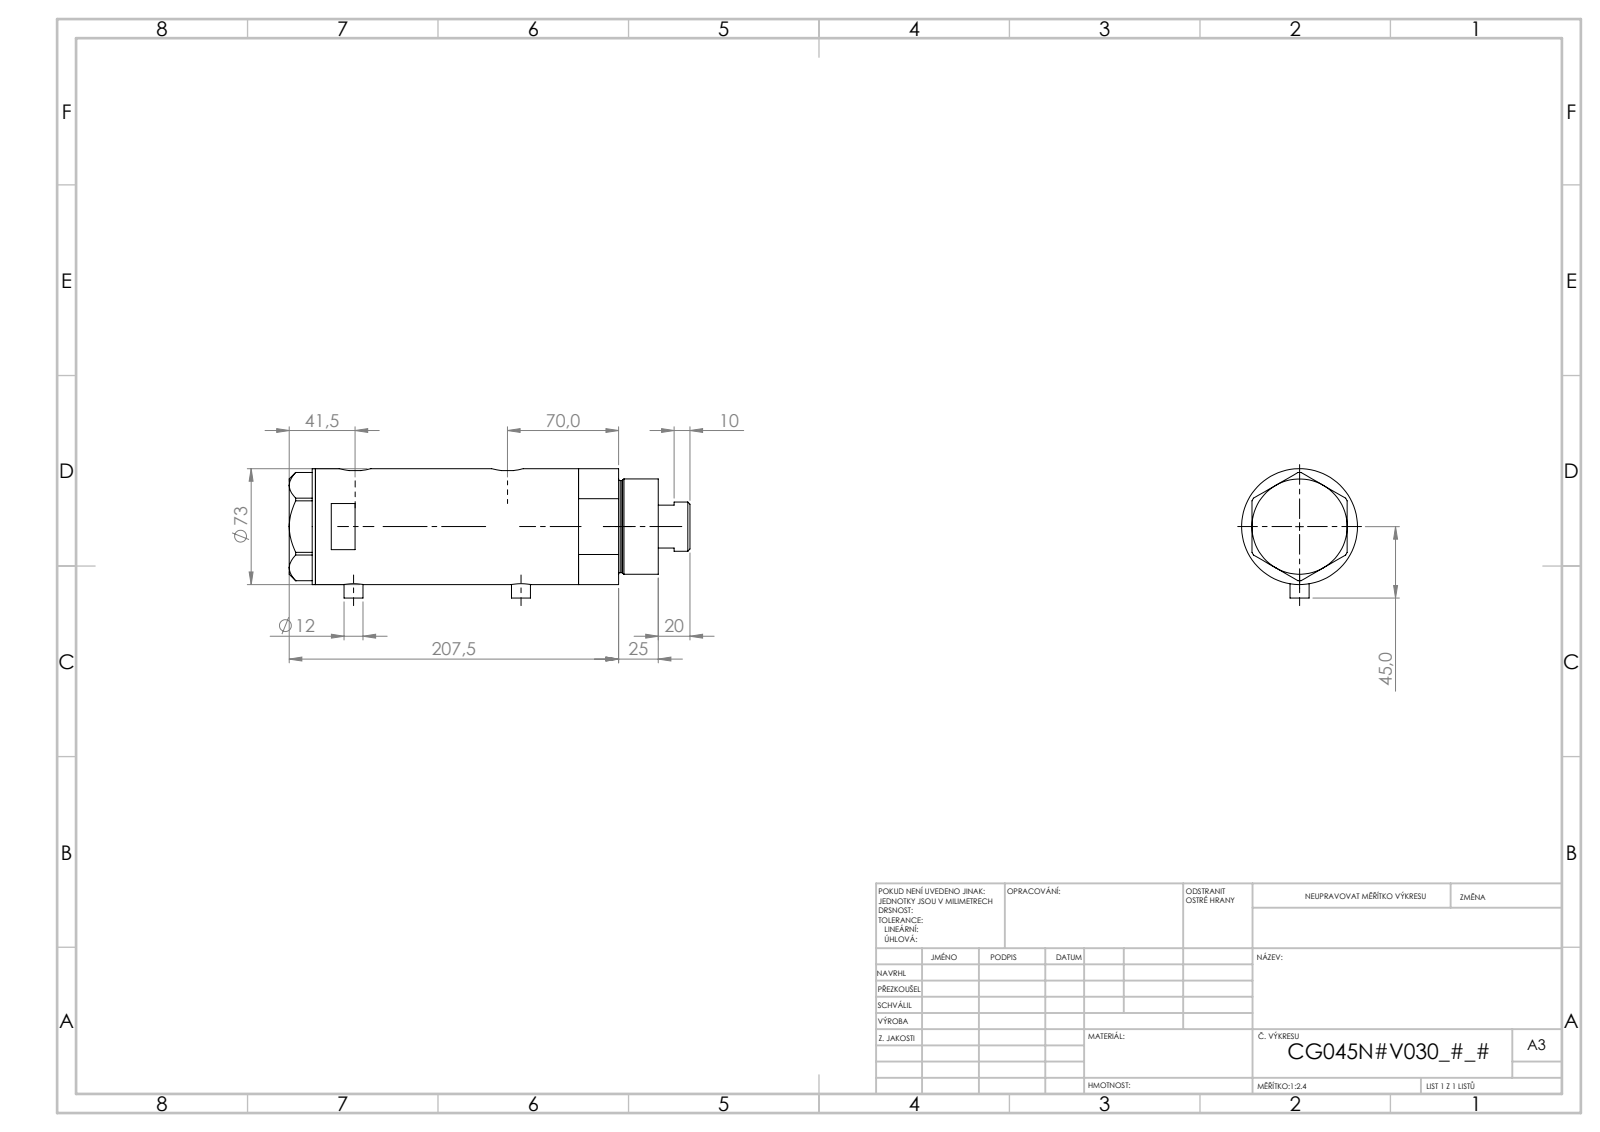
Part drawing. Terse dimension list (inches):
name: V270CG_MIDDLE; V270CG_FRONT; V270CG_VC; V270CG_BACK
written by: SolidWorks 2019 (CONFIG_CONTROL_DESIGN)
unit: in
bodies: 4 solids, 120 faces (49 planar, 51 cylindrical, 20 other)
size: 9.941 × 3.209 × 2.874
volume: 55.04 in³; area: 232.1 in²
holes: 2× ⌀0.492, 2× ⌀0.518, 1× ⌀0.413, 1× ⌀1.26, 1× ⌀1.319, 1× ⌀1.772, 1× ⌀1.89, 1× ⌀2.52
bosses: 2× ⌀0.472, 1× ⌀2.874, 1× ⌀2.362, 1× ⌀2.283, 1× ⌀1.22
rounds: 2× R0.394
face distances: 3.74, 4.764, 1.024, 0.65, 1.673, 5.413, 0.079, 8.504, 9.154, 7.48
hole spacings: 0.039, 0.335, 3.78, 3.819, 4.114, 4.154
